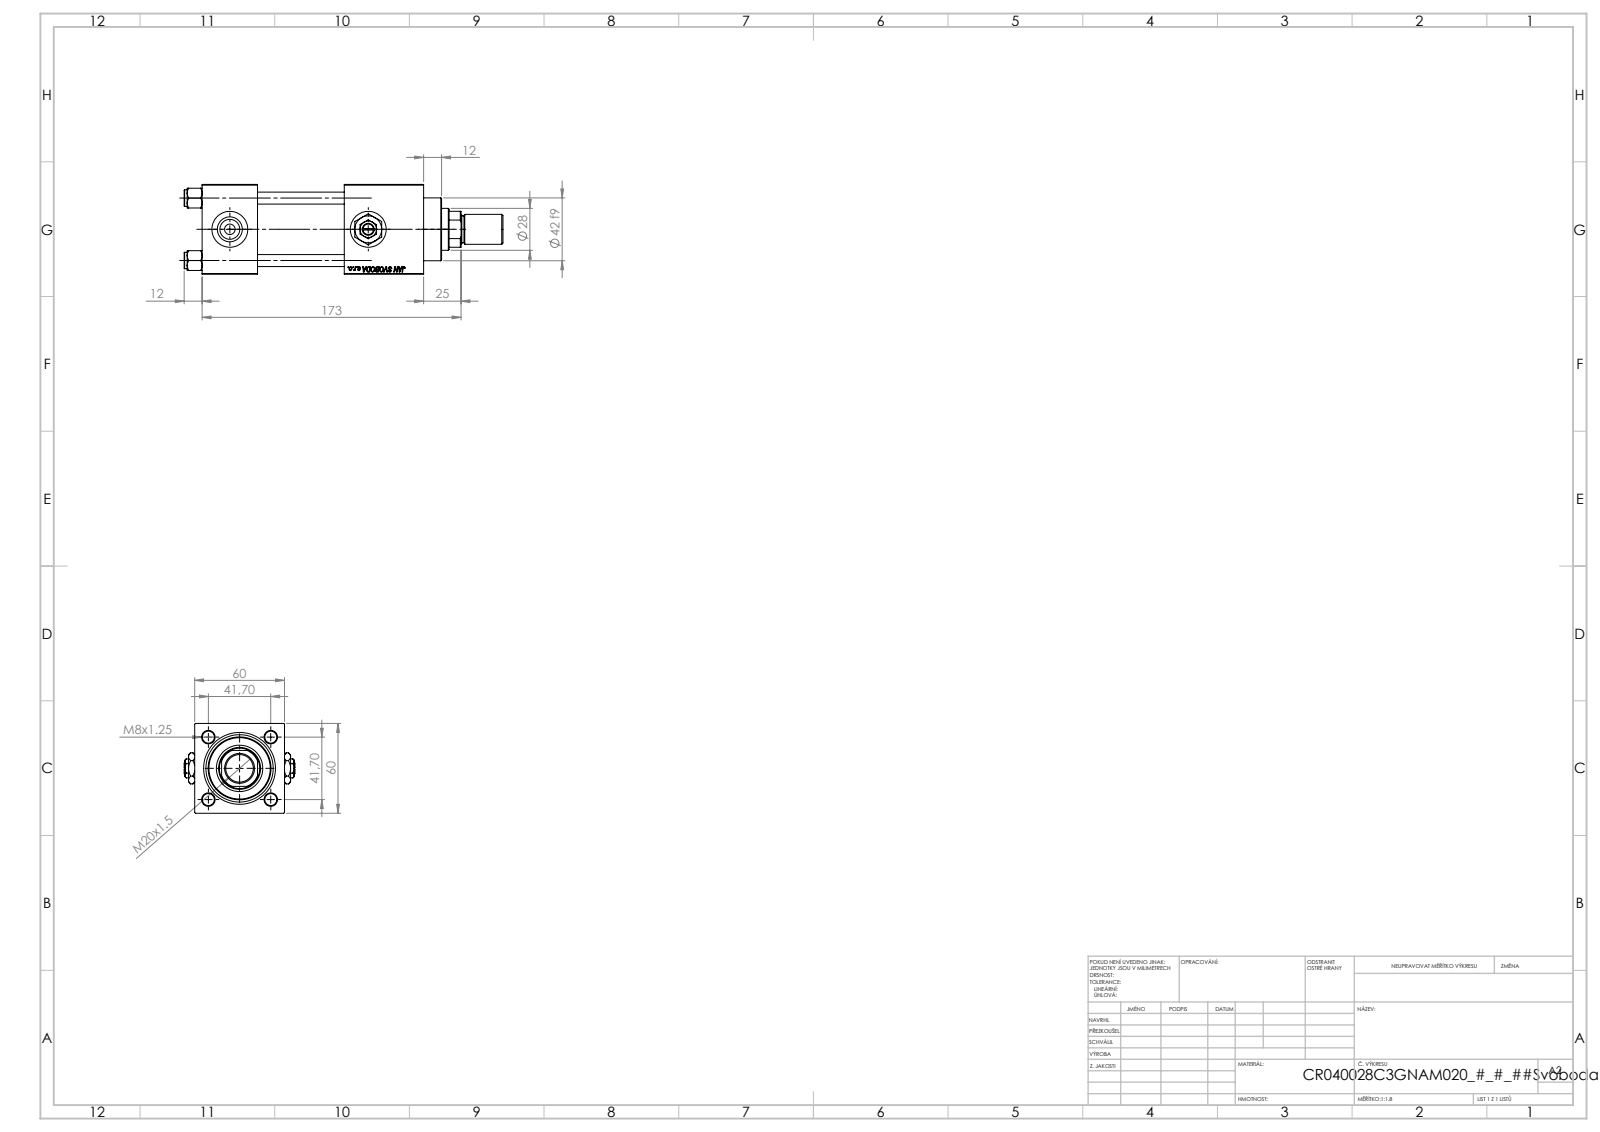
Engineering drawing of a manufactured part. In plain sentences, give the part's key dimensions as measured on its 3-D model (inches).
The part is named "V215_VC_A; Zatka_pro_OIL_PORT; NUT_M5_C; ROD_END_AH (+3 more)". Its 3-D file was written by "SolidWorks 2019 (CONFIG_CONTROL_DESIGN)". It is 14 solids with 1264 faces: 578 planar, 102 cylindrical and 584 other. Overall it measures 8.386 by 2.913 by 2.362 inches. Its volume is 26.22 cubic inches and its surface area 181 square inches. Round holes: 4 of diameter 0.315, 2 of diameter 0.276, 2 of diameter 0.656, 2 of diameter 0.945, 1 of diameter 0.728, 1 of diameter 1.102, 1 of diameter 1.22, 1 of diameter 1.575, 1 of diameter 1.772. Round bosses or shafts: 4 of diameter 0.433, 1 of diameter 1.811, 1 of diameter 1.654, 1 of diameter 0.787, 1 of diameter 0.709. Partial cylindrical surfaces (rounded edges, fillets, slot ends): 1 of radius 0.531. The main face-to-face distances are 2.362, 1.457, 2.283, 2.087, 3.74, 4.697, 3.24, 0.957, 5.827, 4.37. The hole center spacings are 1.161, 1.642, 2.322, 3.642.
